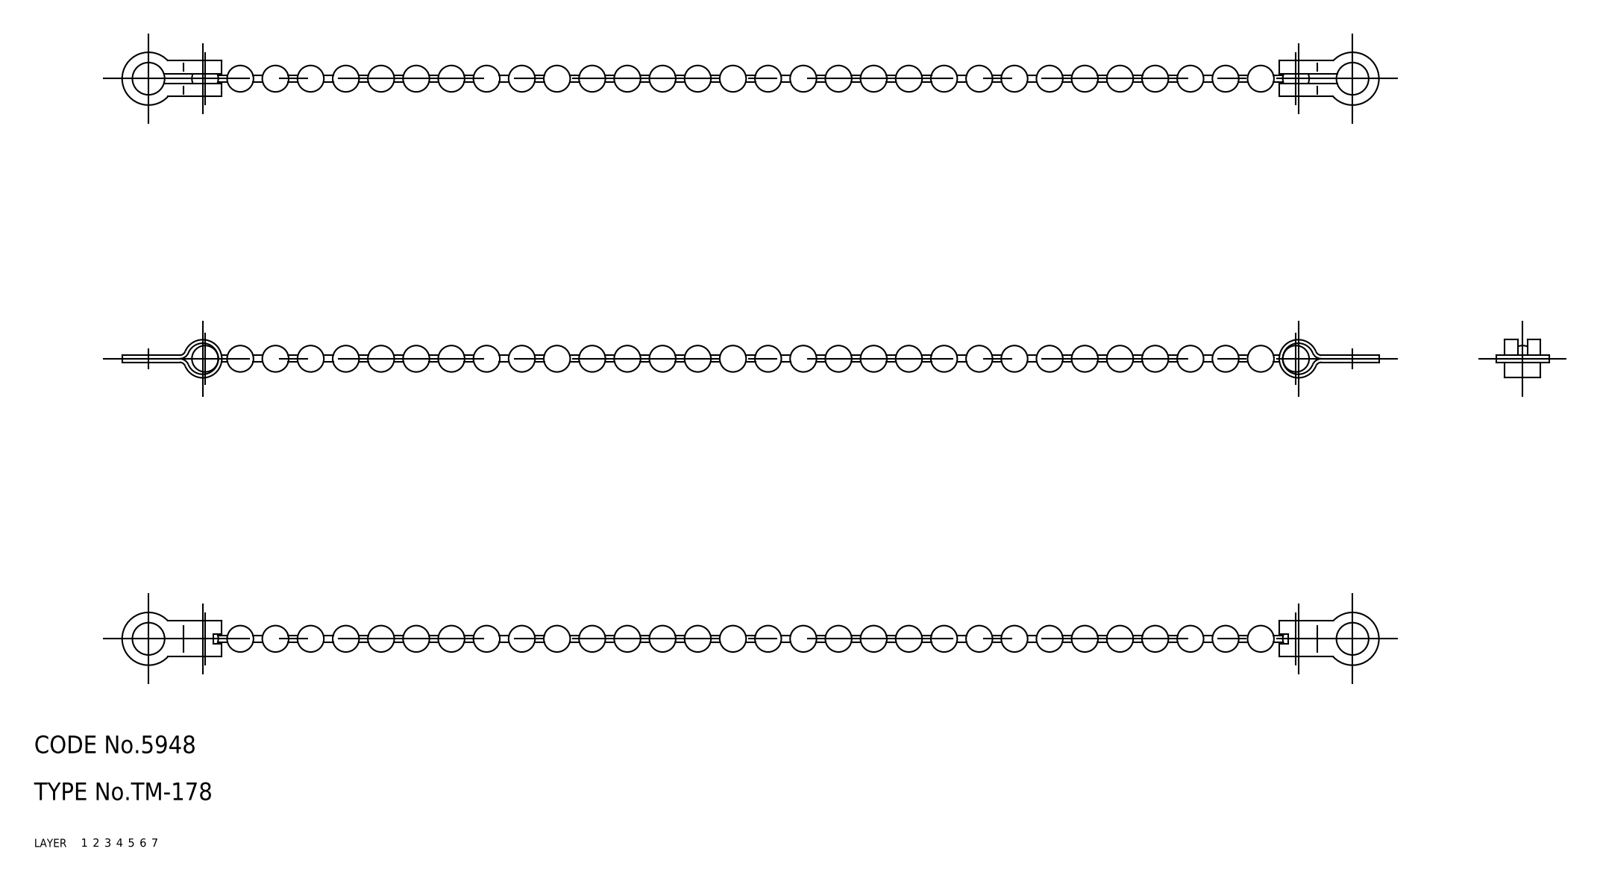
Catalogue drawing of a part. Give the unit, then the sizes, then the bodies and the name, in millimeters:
Units: millimetres
Overall size (bounding box): 214.3 × 9 × 6.5
Volume: 1 728 mm³ · Surface area: 4 139 mm²
Bodies: 35 solids, 144 faces (0 planar, 0 cylindrical, 144 other)
Part name (STEP PRODUCT): 67119442; 67119455; 67119468; 67119481 (+8 more)
STEP written by: CADfix (AUTOMOTIVE_DESIGN)
